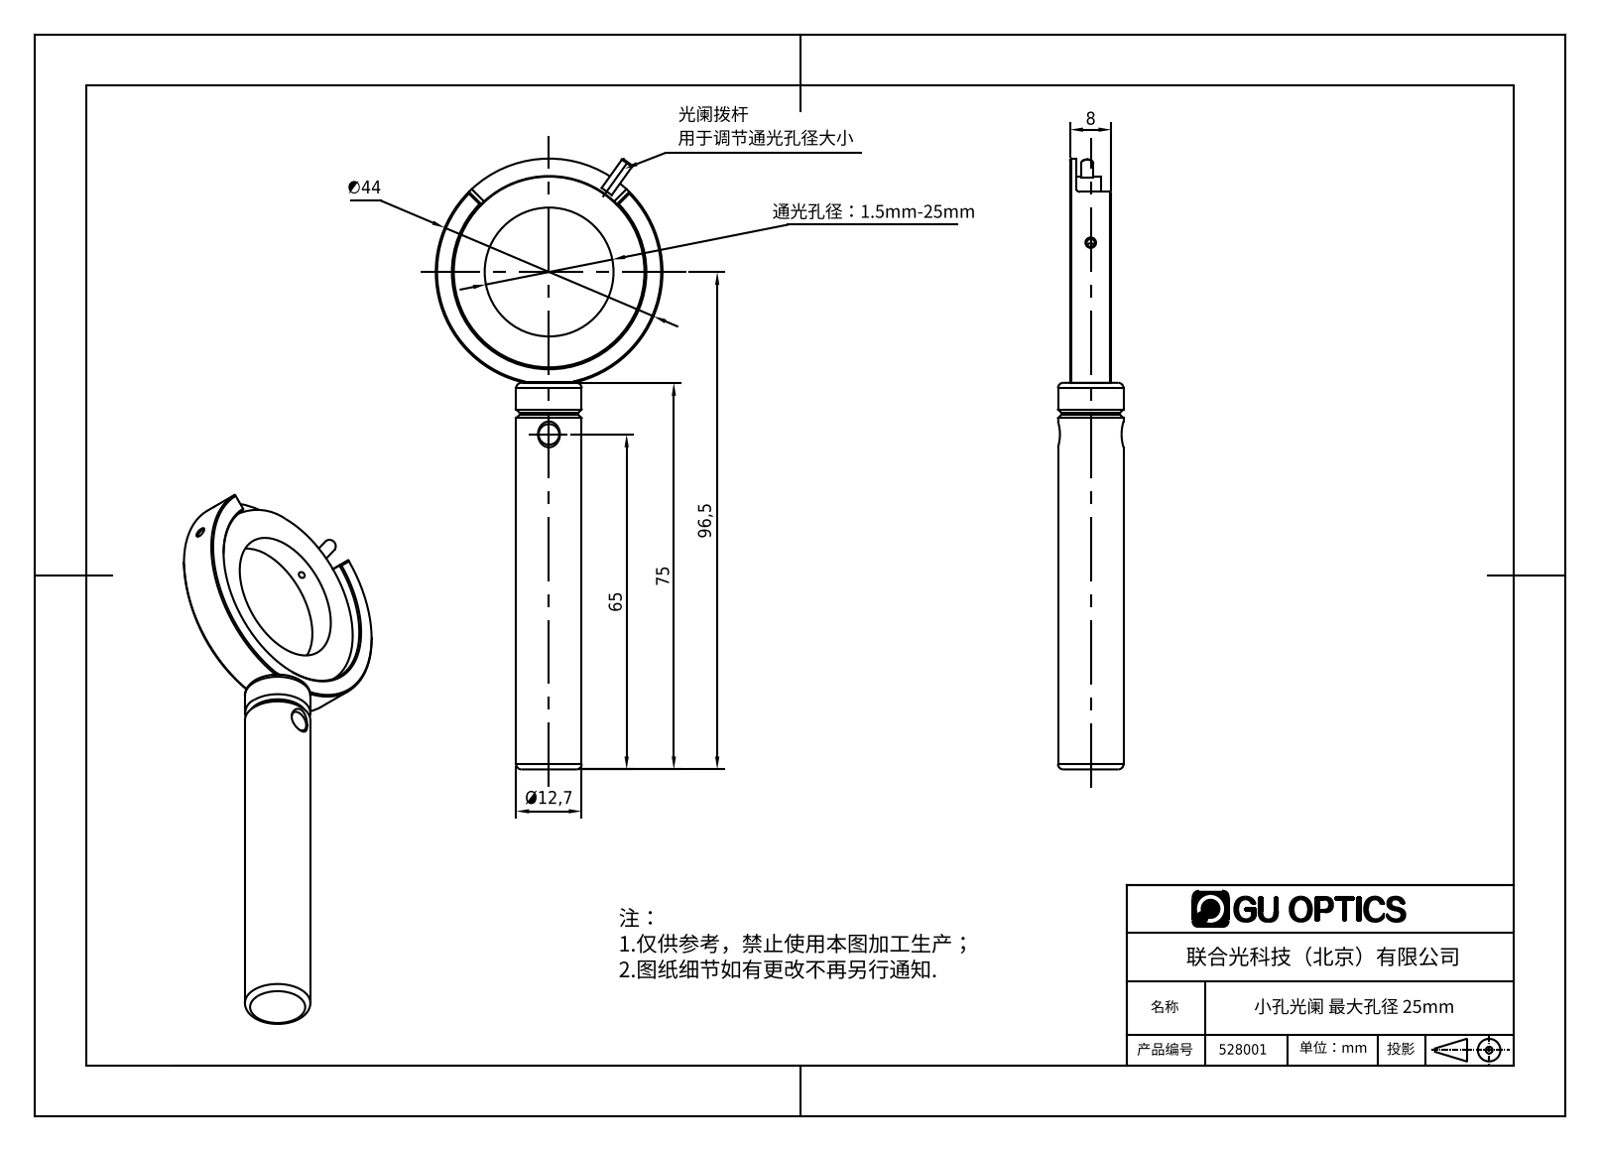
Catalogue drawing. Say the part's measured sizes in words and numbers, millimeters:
The part is named "528001(1)". Its 3-D file was written by "SolidWorks 2020 (CONFIG_CONTROL_DESIGN)". It is 4 solids with 54 faces: 20 planar, 15 cylindrical and 19 other. Overall it measures 118.5 by 44 by 12.7 millimeters. Its volume is 15 022 cubic millimeters and its surface area 8 641 square millimeters. Round holes: 2 of diameter 1.6, 1 of diameter 1.25, 1 of diameter 4, 1 of diameter 25, 1 of diameter 33, 1 of diameter 37.25. Round bosses or shafts: 1 of diameter 44, 1 of diameter 37, 1 of diameter 12.7, 1 of diameter 2.4. Partial cylindrical surfaces (rounded edges, fillets, slot ends): 2 of radius 0.75, 1 of radius 16. The main face-to-face distances are 1, 6.06, 5.06, 8, 7, 1.94, 1.2, 4.86, 6.8, 75. The hole center spacings are 31.5.
